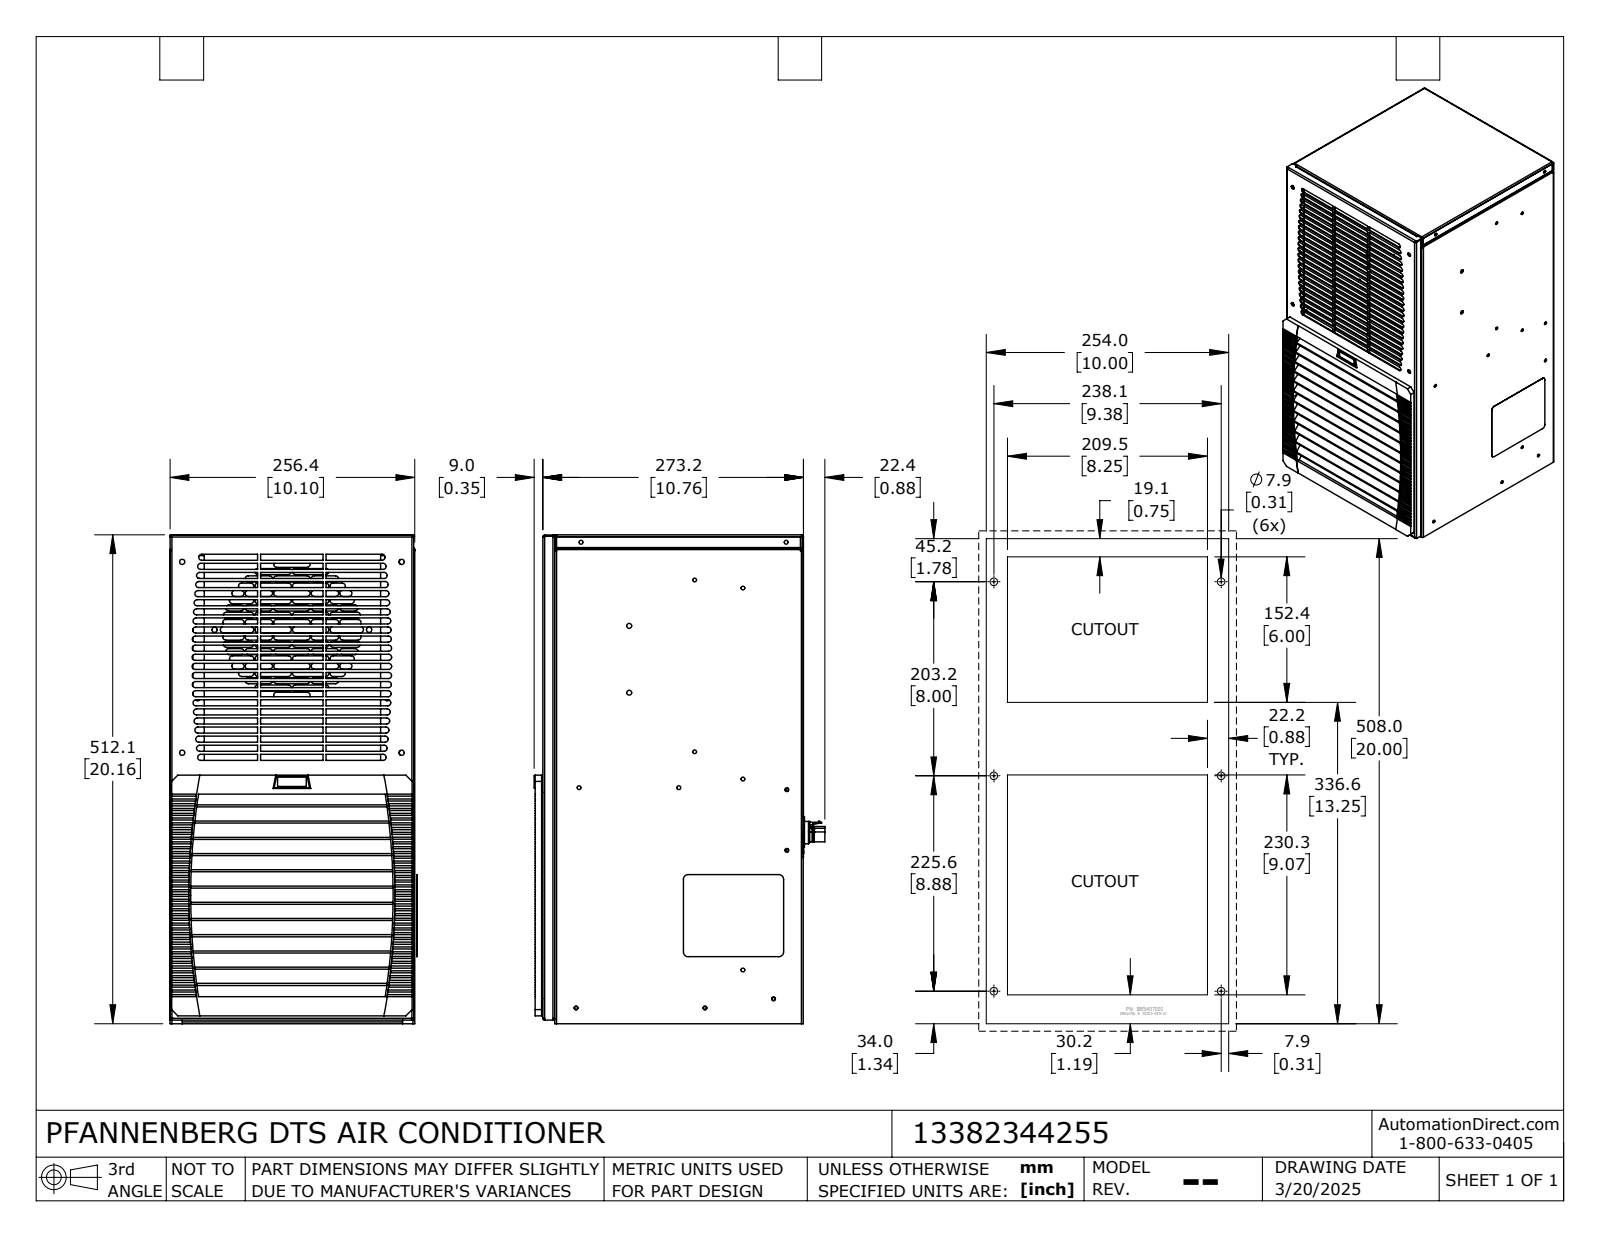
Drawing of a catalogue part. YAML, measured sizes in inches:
part_name: "13382344255_Default"
step_written_by: "SolidWorks 2024 (CONFIG_CONTROL_DESIGN)"
units: inches
bodies: {solids: 11, faces: 2383, planar: 1378, cylindrical: 900, other: 105}
overall_size: [20.16, 11.99, 10.183]
volume: 107.5
surface_area: 2534
round_holes:
  - {diameter: 0.156, count: 12}
  - {diameter: 0.157, count: 12}
  - {diameter: 0.217, count: 12}
  - {diameter: 0.187, count: 8}
  - {diameter: 0.165, count: 6}
  - {diameter: 0.169, count: 5}
  - {diameter: 0.209, count: 5}
  - {diameter: 0.149, count: 4}
  - {diameter: 0.281, count: 4}
  - {diameter: 0.313, count: 4}
  - {diameter: 0.394, count: 4}
  - {diameter: 0.129, count: 3}
round_bosses_or_shafts:
  - {diameter: 0.079, count: 4}
  - {diameter: 1.378, count: 1}
  - {diameter: 1.102, count: 1}
  - {diameter: 0.945, count: 1}
  - {diameter: 0.906, count: 1}
  - {diameter: 0.56, count: 1}
  - {diameter: 0.475, count: 1}
  - {diameter: 0.475, count: 1}
partial_cylinders:
  - {radius: 0.125, count: 186}
  - {radius: 0.118, count: 43}
  - {radius: 0.031, count: 30}
  - {radius: 0.076, count: 30}
  - {radius: 0.049, count: 24}
  - {radius: 0.031, count: 10}
  - {radius: 0.076, count: 10}
  - {radius: 0.079, count: 8}
face_to_face_distances: [0.045, 0.045, 10.006, 10.05, 10.051, 10.096, 10.711, 0.473, 0.057, 10.654]
hole_center_spacings: [0.294, 1.083, 2.5, 2.756, 2.961, 4.921, 7.812, 9.233]
